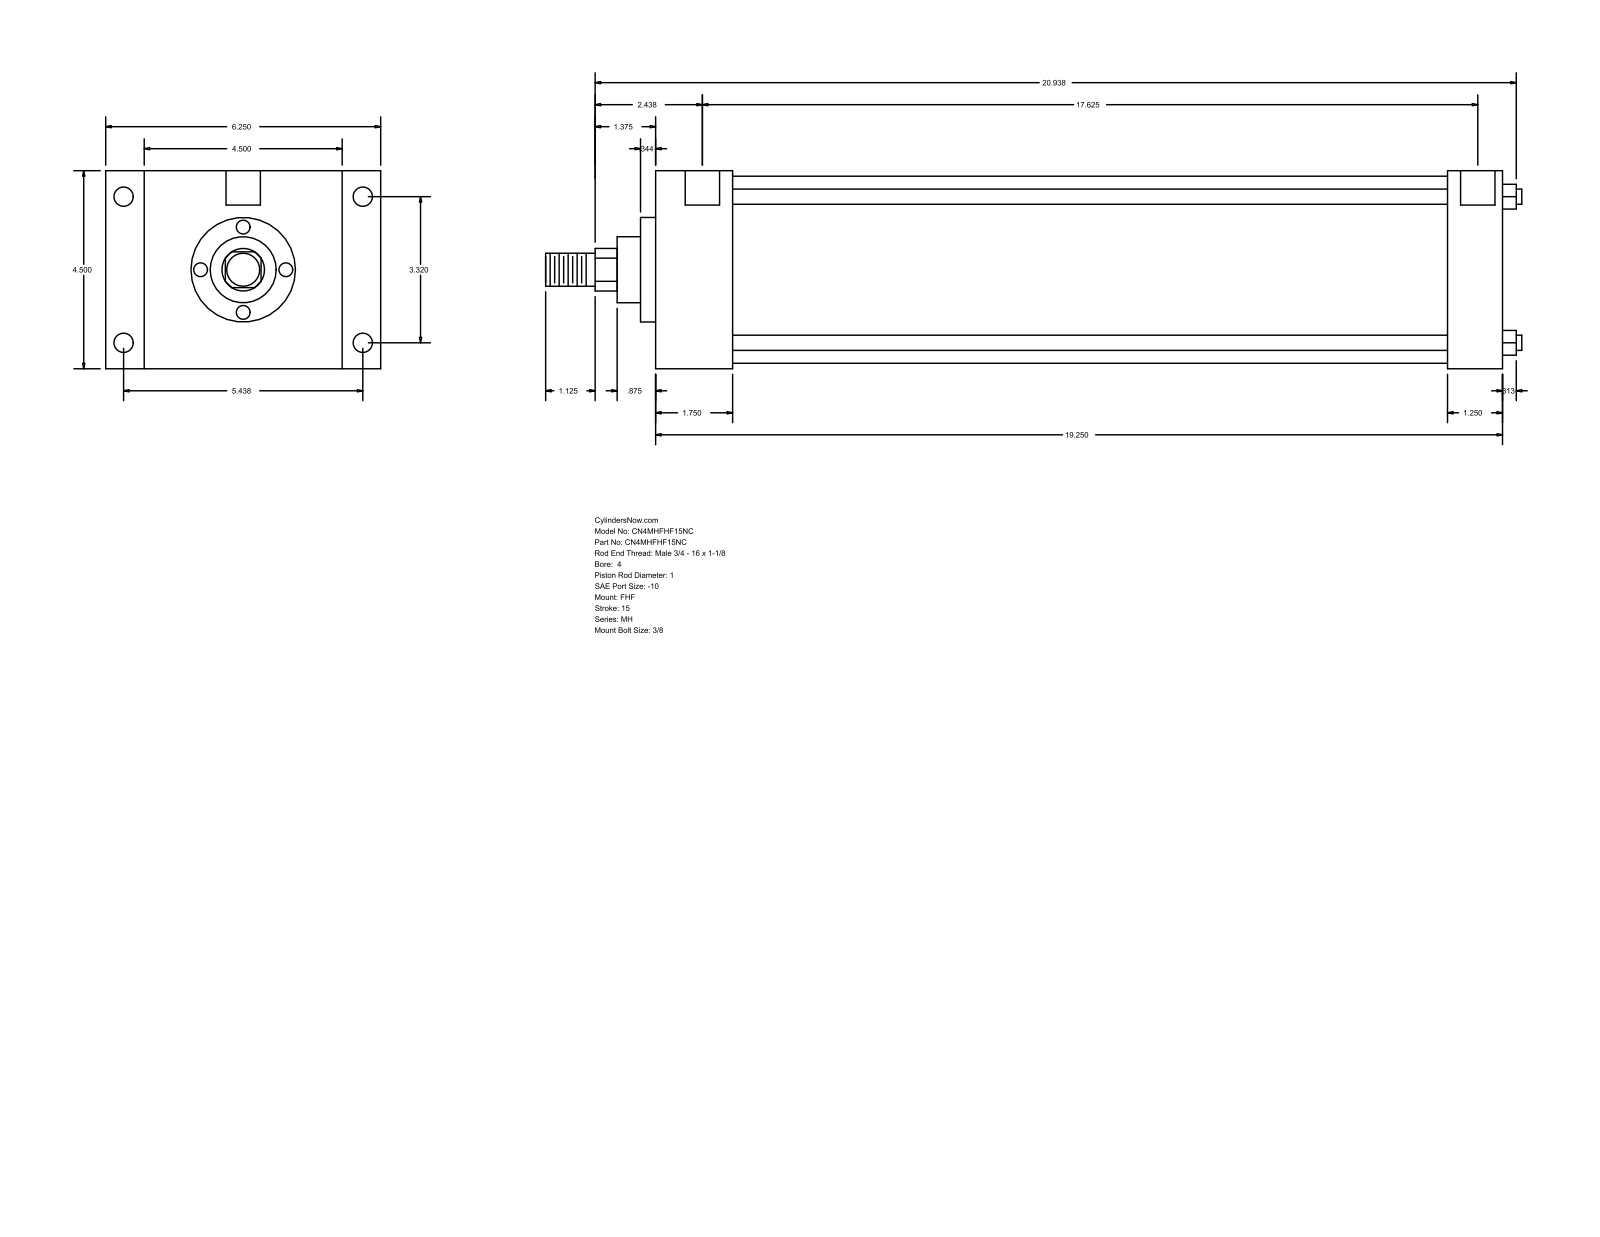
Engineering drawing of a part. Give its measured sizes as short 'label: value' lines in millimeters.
name: MH_FHF__0400_1
written by: GSSL Pune (CONFIG_CONTROL_DESIGN)
unit: mm
bodies: 0 solids, 90 faces (61 planar, 29 cylindrical, 0 other)
size: 563.56 × 158.75 × 114.3
holes: 4× ⌀8.73, 4× ⌀11.13, 2× ⌀19.84
bosses: 4× ⌀8.76, 1× ⌀107.95, 1× ⌀60.33, 1× ⌀38.1, 1× ⌀25.4, 1× ⌀19.05
rounds: 1× R12.29
face distances: 114.3, 488.96, 44.46, 444.5, 22.23, 136.53, 158.76, 457.2, 412.74, 31.76
hole spacings: 84.32, 138.12, 161.82, 450.85, 1.58, 1.59, 447.68, 449.26
